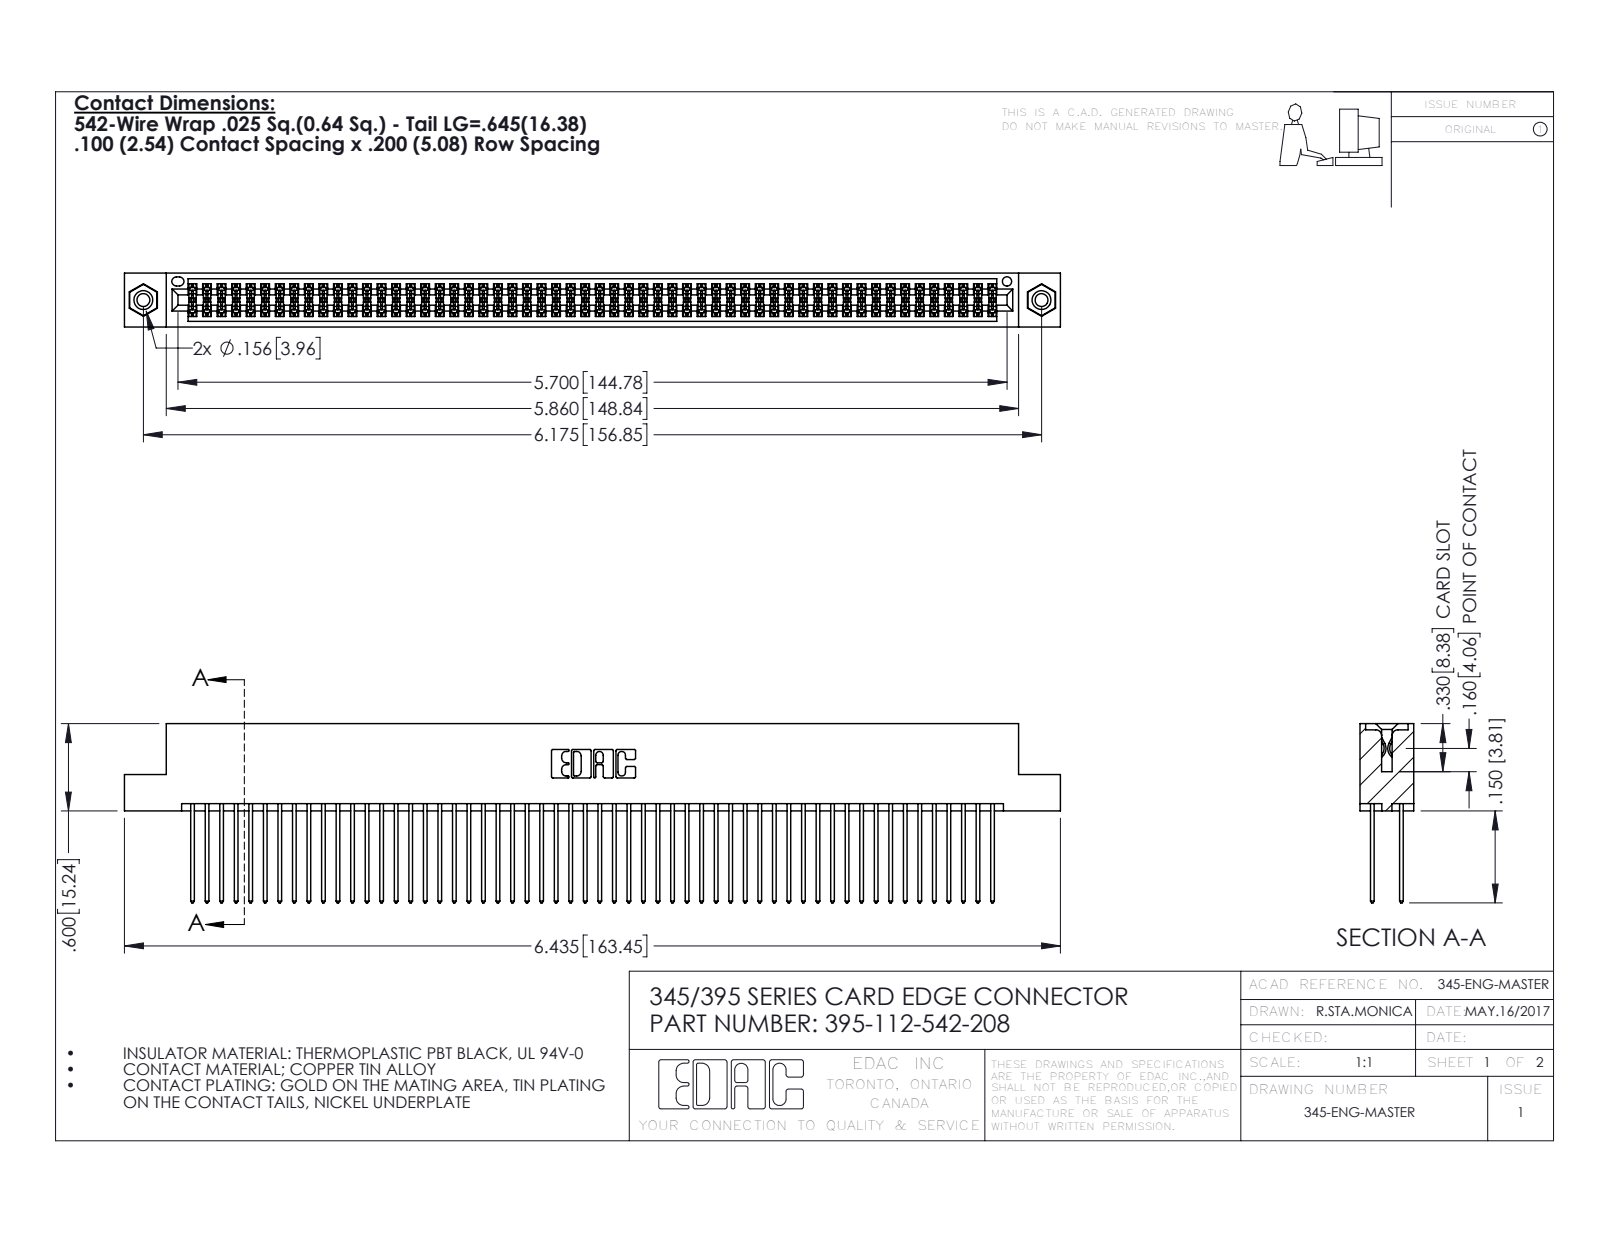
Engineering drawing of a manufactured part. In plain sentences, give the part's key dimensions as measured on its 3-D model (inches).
The part is named "345 Part_Flush Mounting Lugs - 0.156 Dia-TI; 345-292-001_345-293-142; 345-250-001_345-250-003-102; 395-112-542-208". Its 3-D file was written by "SolidWorks 2016 (CONFIG_CONTROL_DESIGN)". It is 115 solids with 5786 faces: 3808 planar, 1962 cylindrical and 16 other. Overall it measures 6.435 by 1.232 by 0.37 inches. Its volume is 1.008 cubic inches and its surface area 42.08 square inches. Round holes: 2 of diameter 0.089, 2 of diameter 0.125, 2 of diameter 0.156, 1 of diameter 0.064. Round bosses or shafts: 2 of diameter 0.155. Partial cylindrical surfaces (rounded edges, fillets, slot ends): 168 of radius 0.006, 112 of radius 0.01, 22 of radius 0.01, 6 of radius 0.007, 6 of radius 0.031, 3 of radius 0.026, 2 of radius 0.014, 2 of radius 0.019. The main face-to-face distances are 0.072, 0.298, 0.2, 0.098, 0.272, 0.025, 0.225, 0.37, 0.175, 0.149. The hole center spacings are 0.27, 5.939, 6.175.
